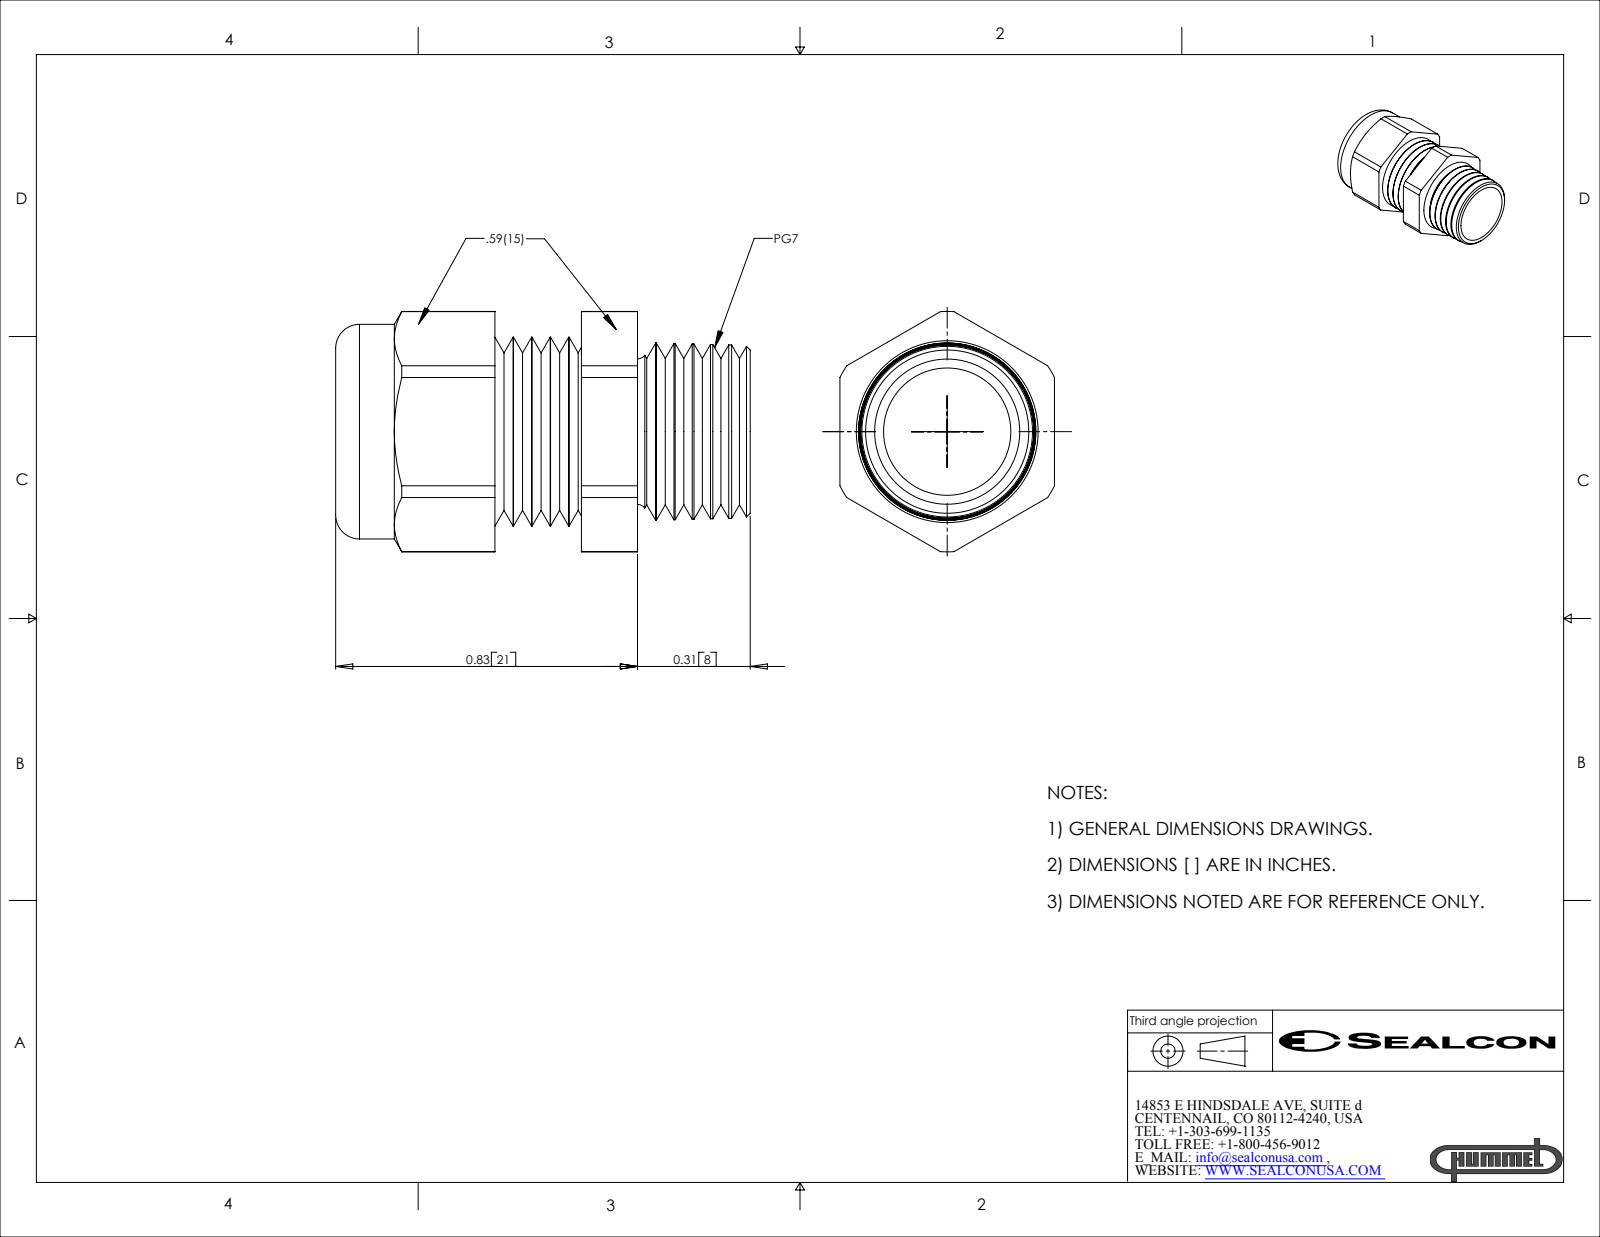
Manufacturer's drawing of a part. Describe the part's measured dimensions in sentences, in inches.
The part is named "CD07AA-GY". Its 3-D file was written by "SolidWorks 2007 (CONFIG_CONTROL_DESIGN)". It is 2 solids with 124 faces: 20 planar, 32 cylindrical and 72 other. Overall it measures 1.14 by 0.661 by 0.59 inches. Its volume is 0.14 cubic inches and its surface area 5.059 square inches. Round holes: 1 of diameter 0.35, 1 of diameter 0.417. Round bosses or shafts: 1 of diameter 0.59, 1 of diameter 0.519. Partial cylindrical surfaces (rounded edges, fillets, slot ends): 1 of radius 0.33. The main face-to-face distances are 0.59, 0.392, 0.238, 0.154, 0.277, 0.515, 0.669, 0.979, 0.702, 0.464.
